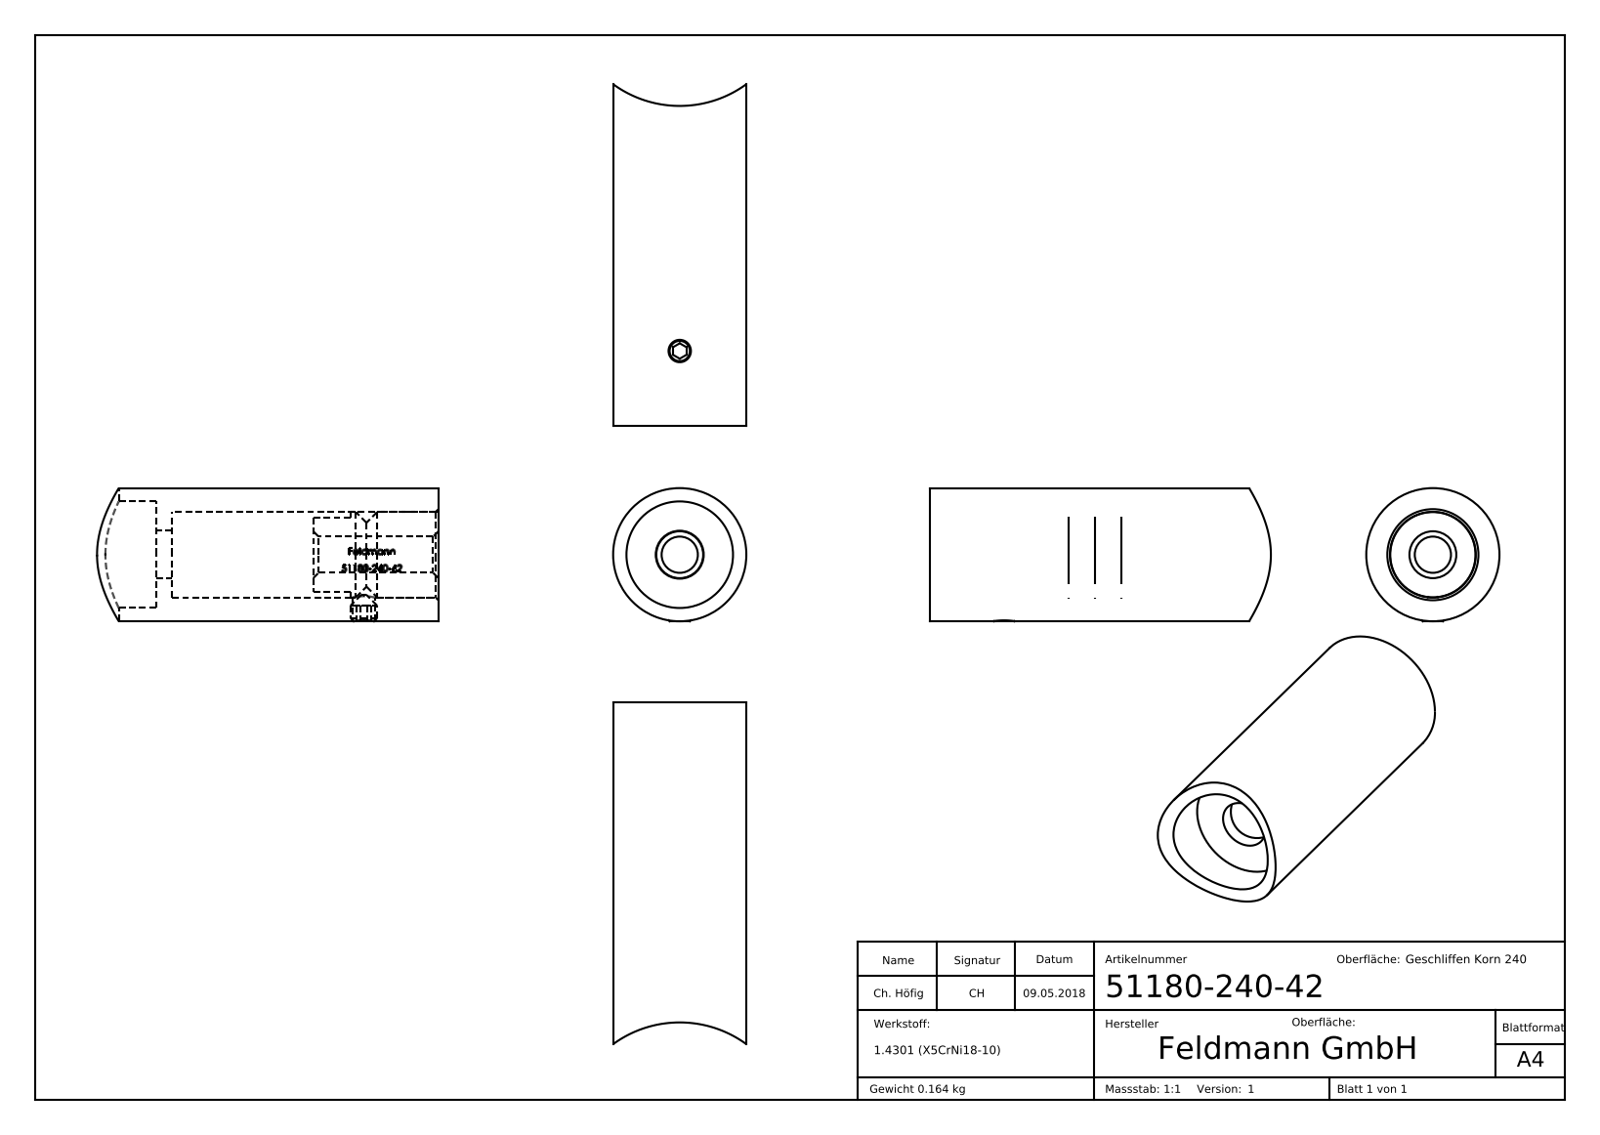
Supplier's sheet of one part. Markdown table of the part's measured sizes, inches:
| quantity | value |
| --- | --- |
| part name | 5x180-240-xx Konfig Teil1_51180-240-42 Teil1; DIN914_DIN 914 M5x5; 5x180-240-xx Konfig Teil2_5x180-240-xx Teil2; 51180-240-42 |
| STEP written by | SolidWorks 2015 (CONFIG_CONTROL_DESIGN) |
| units | inches |
| bodies | 3 solids, 307 faces (136 planar, 54 cylindrical, 117 other) |
| overall size | 2.523 × 0.984 × 0.984 |
| volume | 1.296 in³ |
| surface area | 17.01 in² |
| round holes (diameter × count) | 0.165 × 1, 0.268 × 1, 0.354 × 1, 0.634 × 1, 0.787 × 1 |
| round bosses / shafts (diameter × count) | 0.984 × 1, 0.63 × 1, 0.197 × 1 |
| partial cylindrical surfaces (radius × count) | 0.321 × 1, 0.835 × 1 |
| main face-to-face distances | 2.165, 0.197, 1.969, 0.925, 1.043, 1.24, 0.551, 0.098, 0.65, 0.276 |
